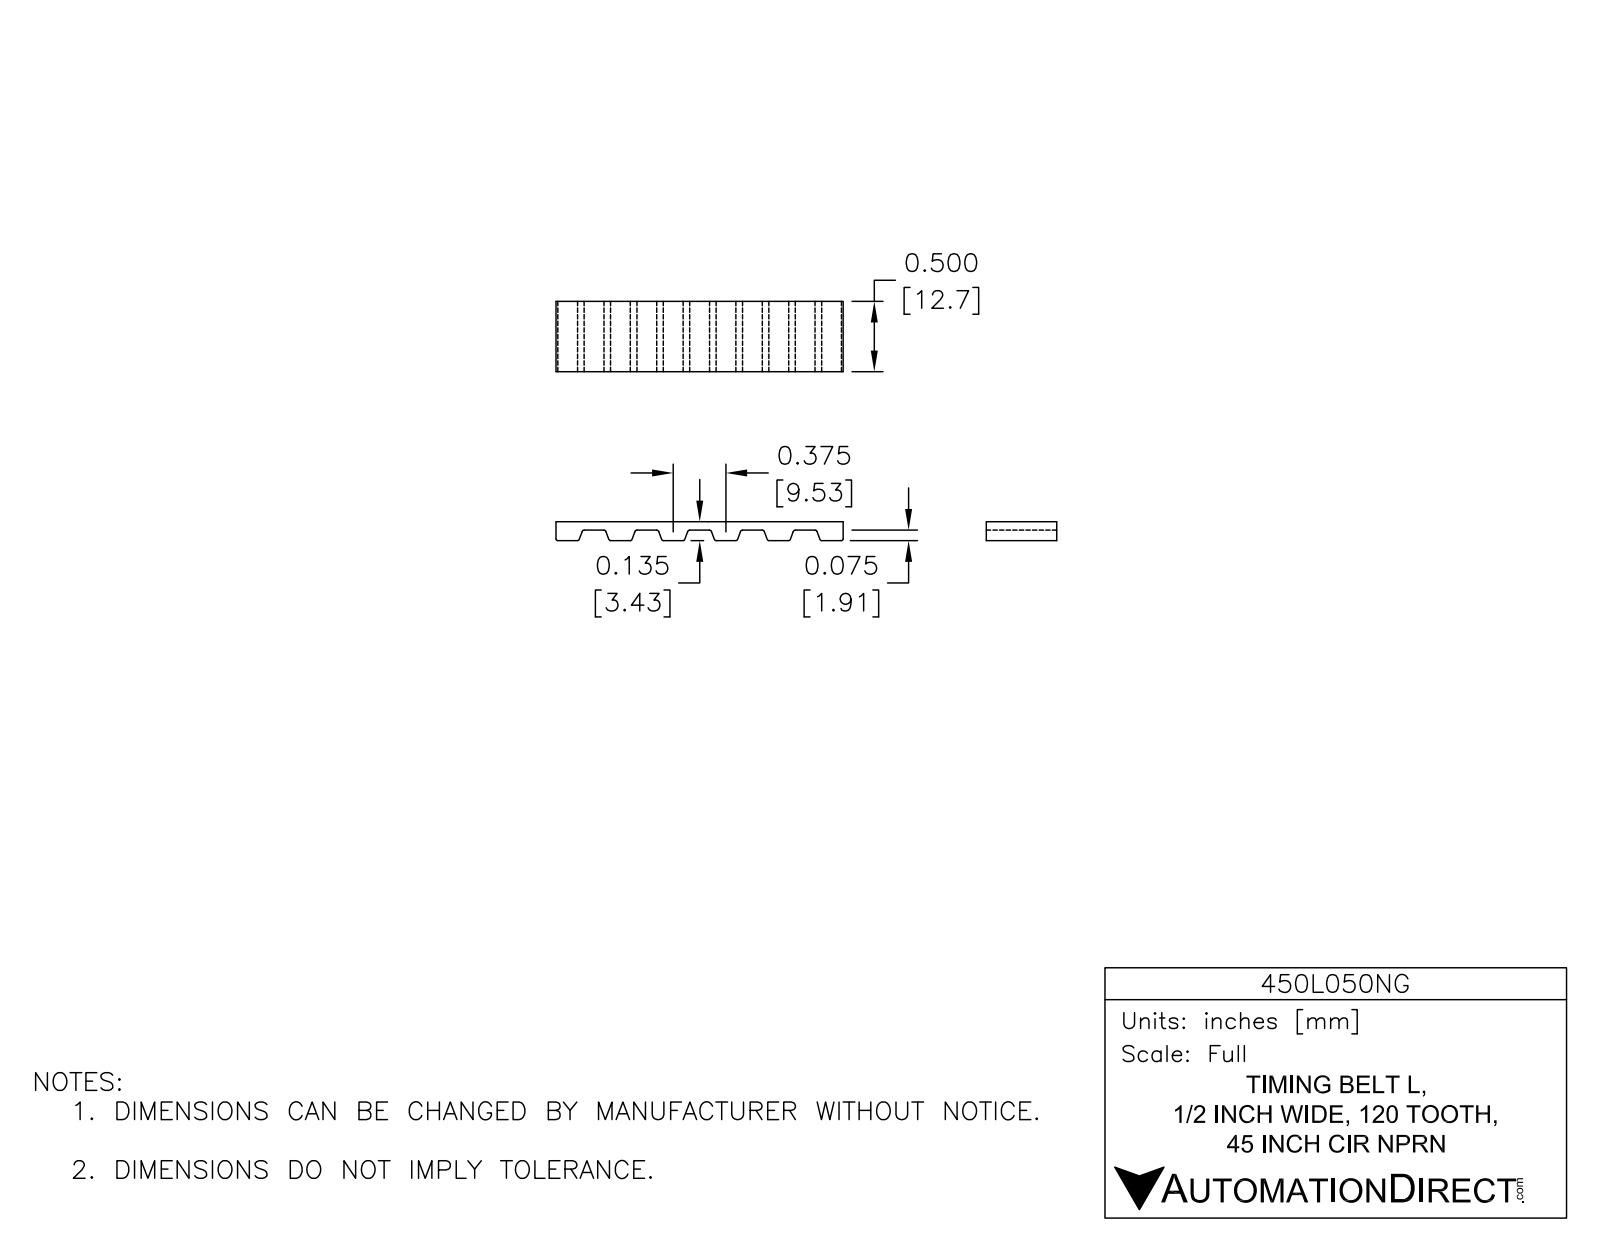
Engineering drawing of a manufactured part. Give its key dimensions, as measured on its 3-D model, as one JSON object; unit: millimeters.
{"part_name": "450L050NG", "step_written_by": "SolidWorks 2014 (AUTOMOTIVE_DESIGN)", "units": "millimeters", "bodies": {"solids": 1, "faces": 976, "planar": 457, "cylindrical": 519, "other": 0}, "overall_size": [528, 76.2, 12.7], "volume_mm3": 33460, "surface_area_mm2": 37650, "partial_cylinders_radius": [[0.5, 476], [36.4, 2], [38.1, 2]], "face_to_face_distances": [1.7, 74.5, 76.2, 72.9, 12.7, 3.6, 72.6, 1.9, 71, 69.1]}
